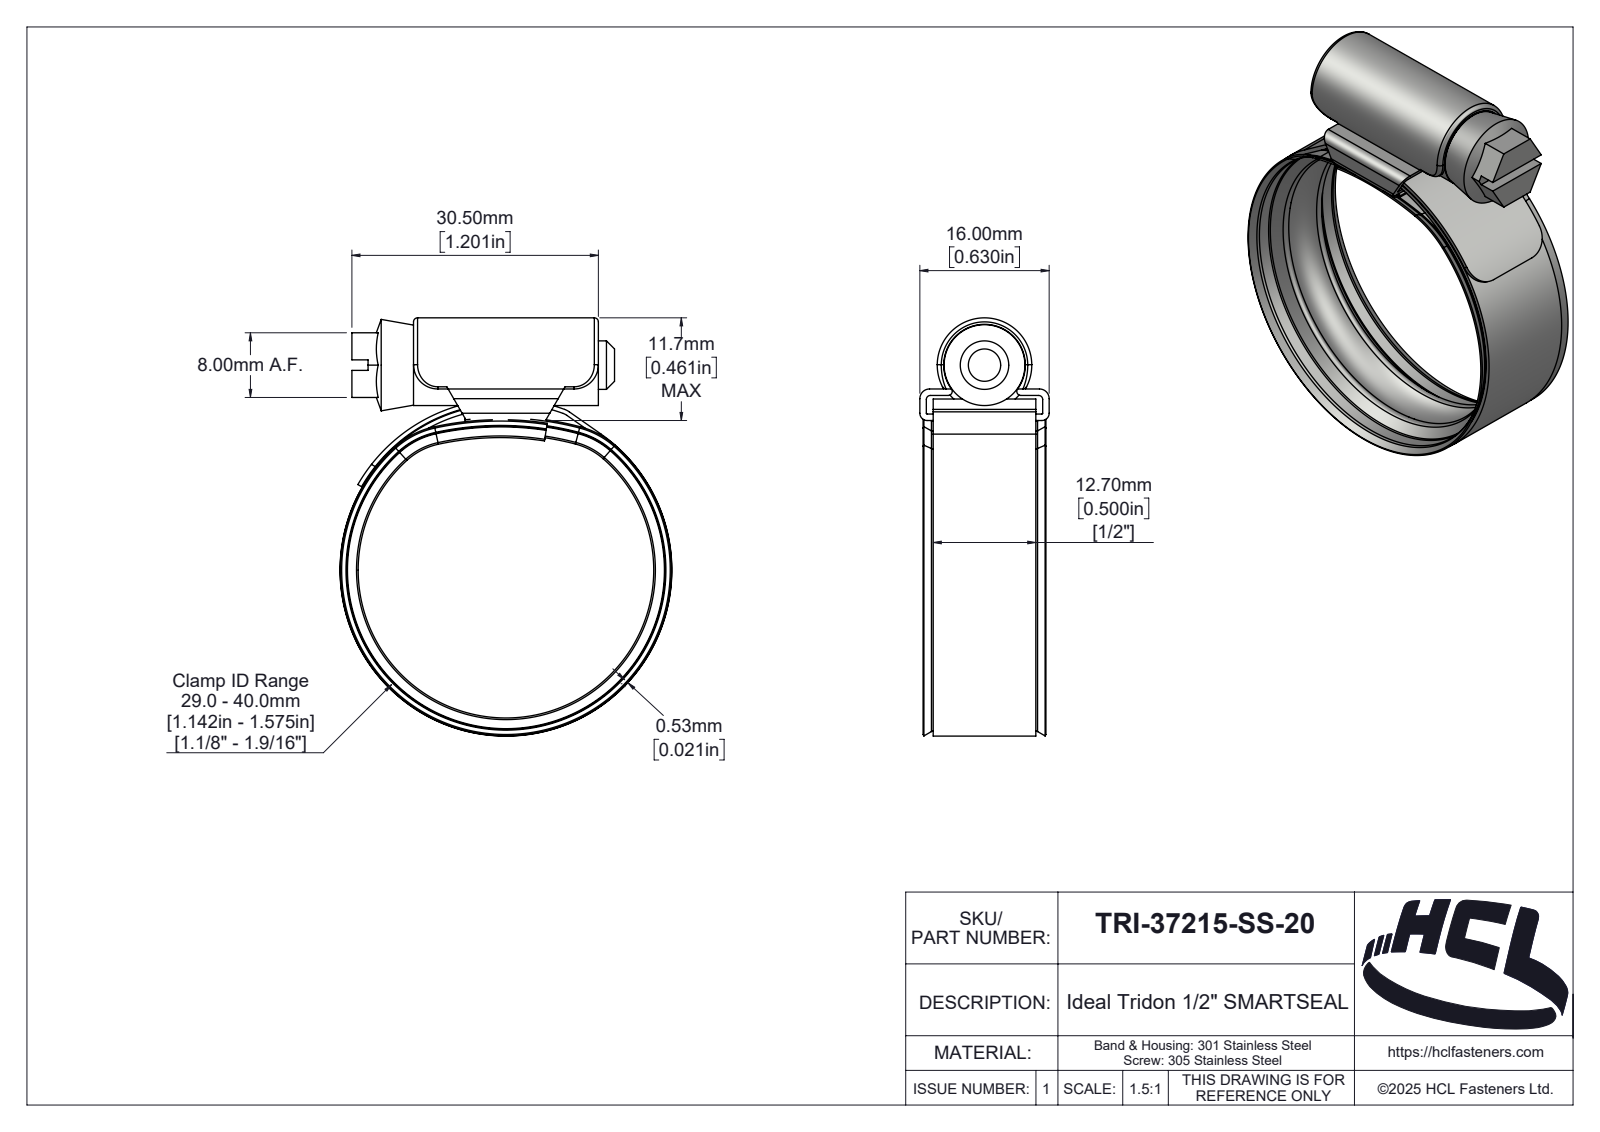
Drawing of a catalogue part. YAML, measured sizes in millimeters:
part_name: "TRI-37215-SS-20"
step_written_by: "SolidWorks 2025 (AUTOMOTIVE_DESIGN)"
units: millimeters
bodies: {solids: 4, faces: 418, planar: 42, cylindrical: 119, other: 257}
overall_size: [51.73, 41.06, 16]
volume: 4503
surface_area: 11392
round_holes:
  - {diameter: 40, count: 1}
round_bosses_or_shafts:
  - {diameter: 41.06, count: 1}
  - {diameter: 10, count: 1}
  - {diameter: 6, count: 1}
partial_cylinders:
  - {radius: 0.5, count: 6}
  - {radius: 3, count: 4}
  - {radius: 0.1, count: 2}
  - {radius: 0.9, count: 2}
  - {radius: 1.2, count: 2}
  - {radius: 9.9, count: 2}
  - {radius: 10.1, count: 2}
  - {radius: 0.46, count: 1}
face_to_face_distances: [0.8, 3.1, 12.7, 2.3, 0.53, 30.5, 3.9, 1.65, 14.35, 15.2]
